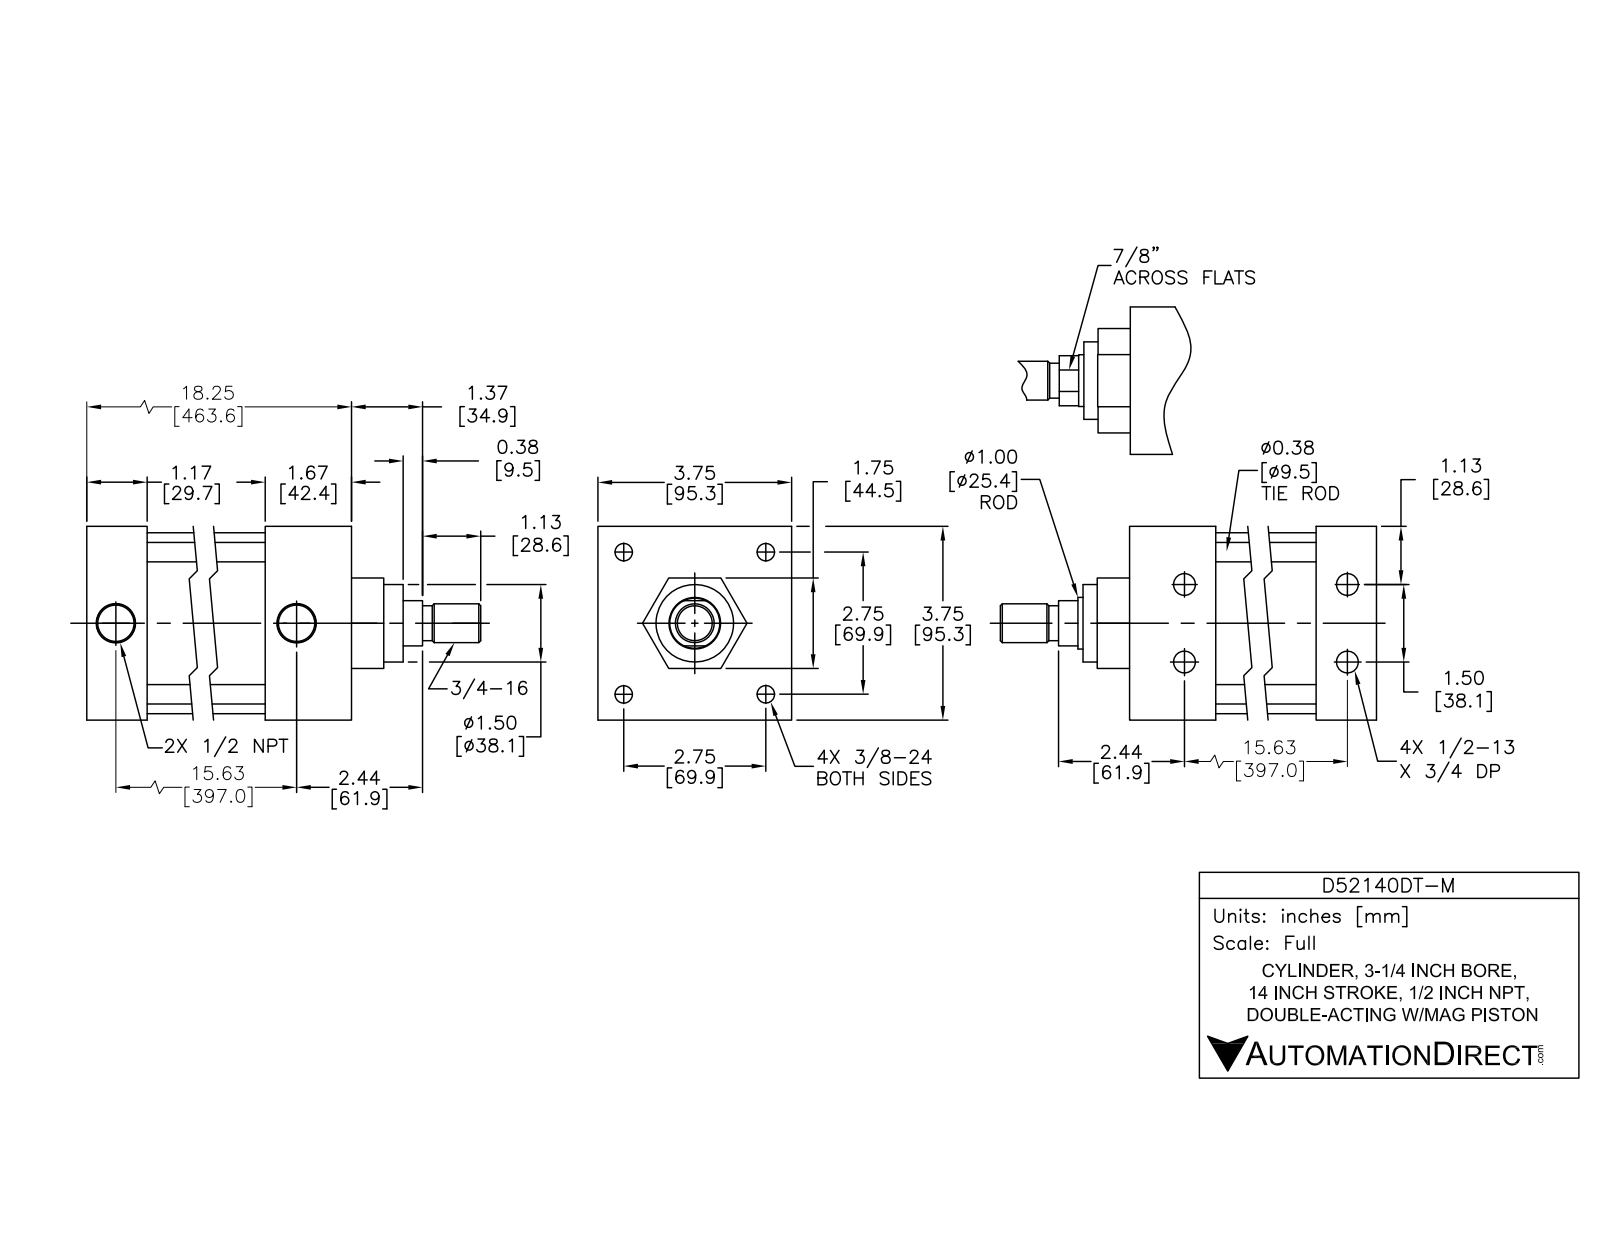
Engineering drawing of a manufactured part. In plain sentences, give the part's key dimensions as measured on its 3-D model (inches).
The part is named "D52140DT-M BODY; D52140DT-M; D52140DT-M PISTON". Its 3-D file was written by "SolidWorks 2015 (AUTOMOTIVE_DESIGN)". It is 12 solids with 303 faces: 99 planar, 114 cylindrical and 90 other. Overall it measures 20.745 by 3.75 by 3.75 inches. Its volume is 88.4 cubic inches and its surface area 637.6 square inches. Round holes: 4 of diameter 0.33, 4 of diameter 0.406, 4 of diameter 0.417, 4 of diameter 0.625, 2 of diameter 0.5, 2 of diameter 0.766, 1 of diameter 1, 1 of diameter 1.003, 1 of diameter 3.25. Round bosses or shafts: 4 of diameter 0.609, 4 of diameter 0.375, 4 of diameter 0.34, 1 of diameter 3.5, 1 of diameter 3.247, 1 of diameter 1.75, 1 of diameter 0.997, 1 of diameter 0.97. Partial cylindrical surfaces (rounded edges, fillets, slot ends): 4 of radius 0.375. The main face-to-face distances are 3.75, 0.08, 15.326, 18.246, 1.75, 16.997, 1.249, 15.751, 1.246, 2.495. The hole center spacings are 0.75, 0.76, 1.5, 1.95, 1.95, 2.758, 2.758, 3.9.
